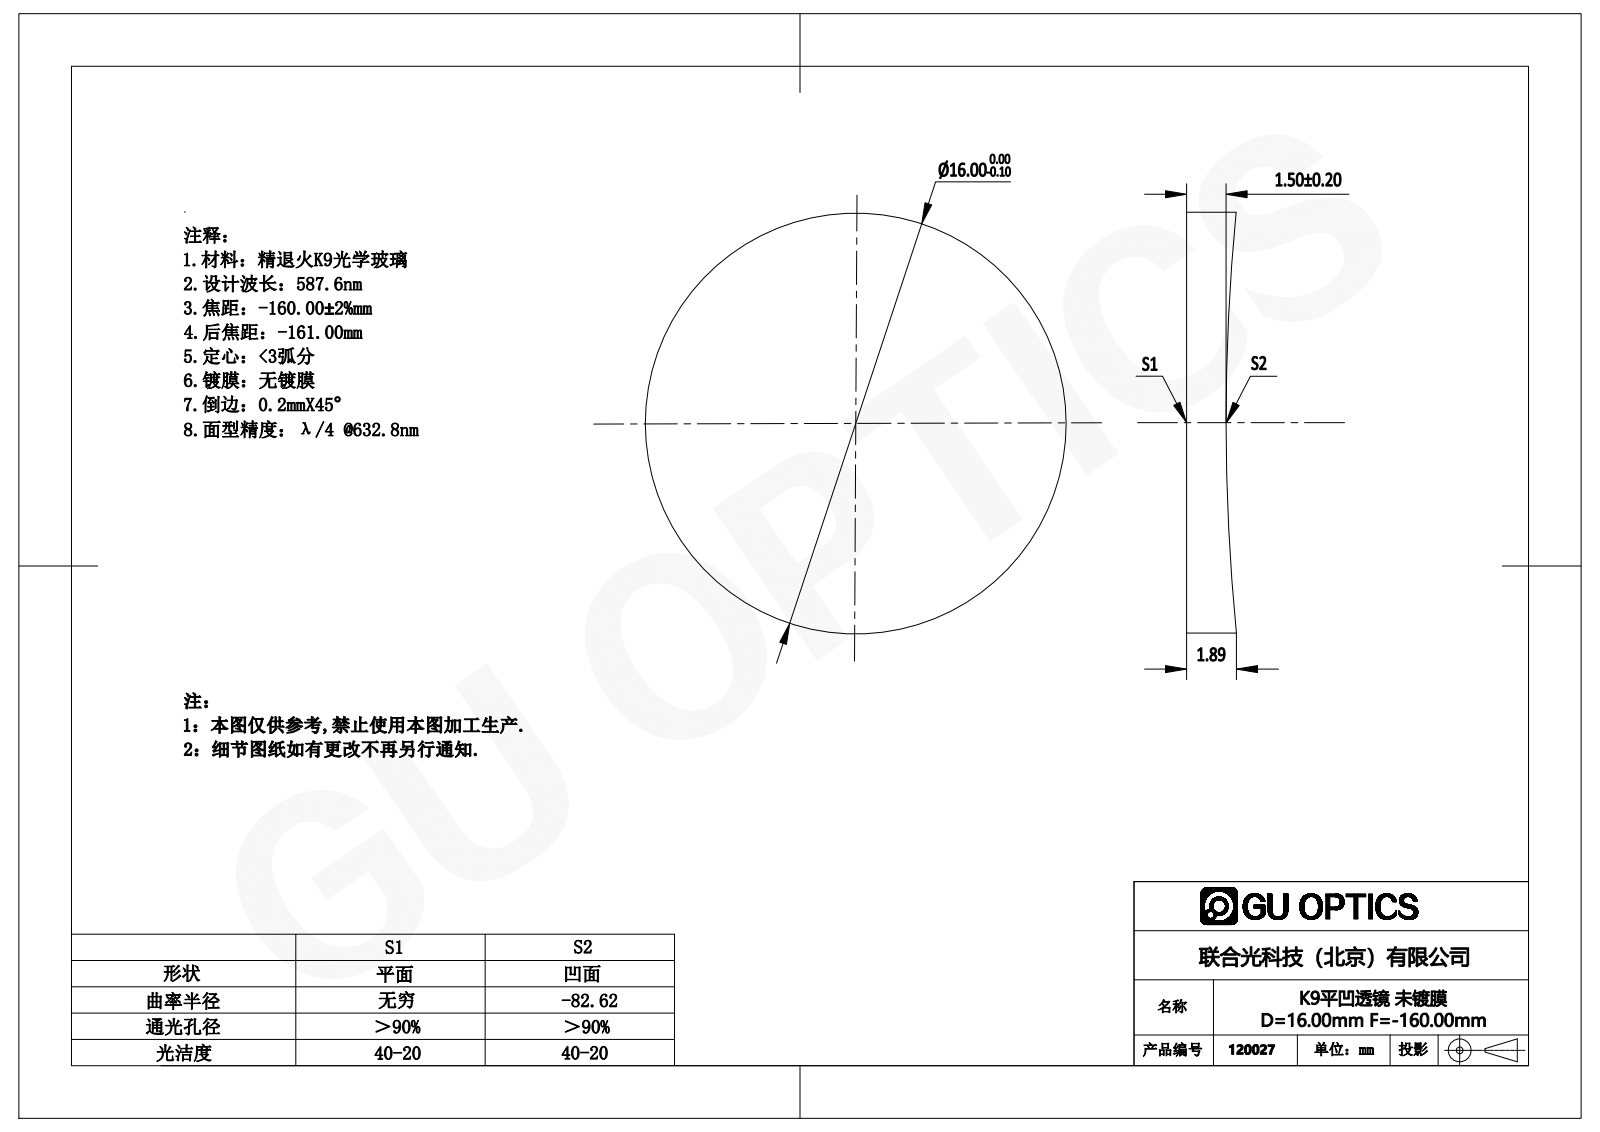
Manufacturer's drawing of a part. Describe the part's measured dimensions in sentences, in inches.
The part is named "120027". Its 3-D file was written by "SolidWorks 2016 (AUTOMOTIVE_DESIGN)". It is 1 solid with 5 faces: 1 planar, 2 cylindrical and 2 other. Overall it measures 0.63 by 0.63 by 0.074 inches. Its volume is 0.021 cubic inches and its surface area 0.77 square inches. Round bosses or shafts: 1 of diameter 0.63.
